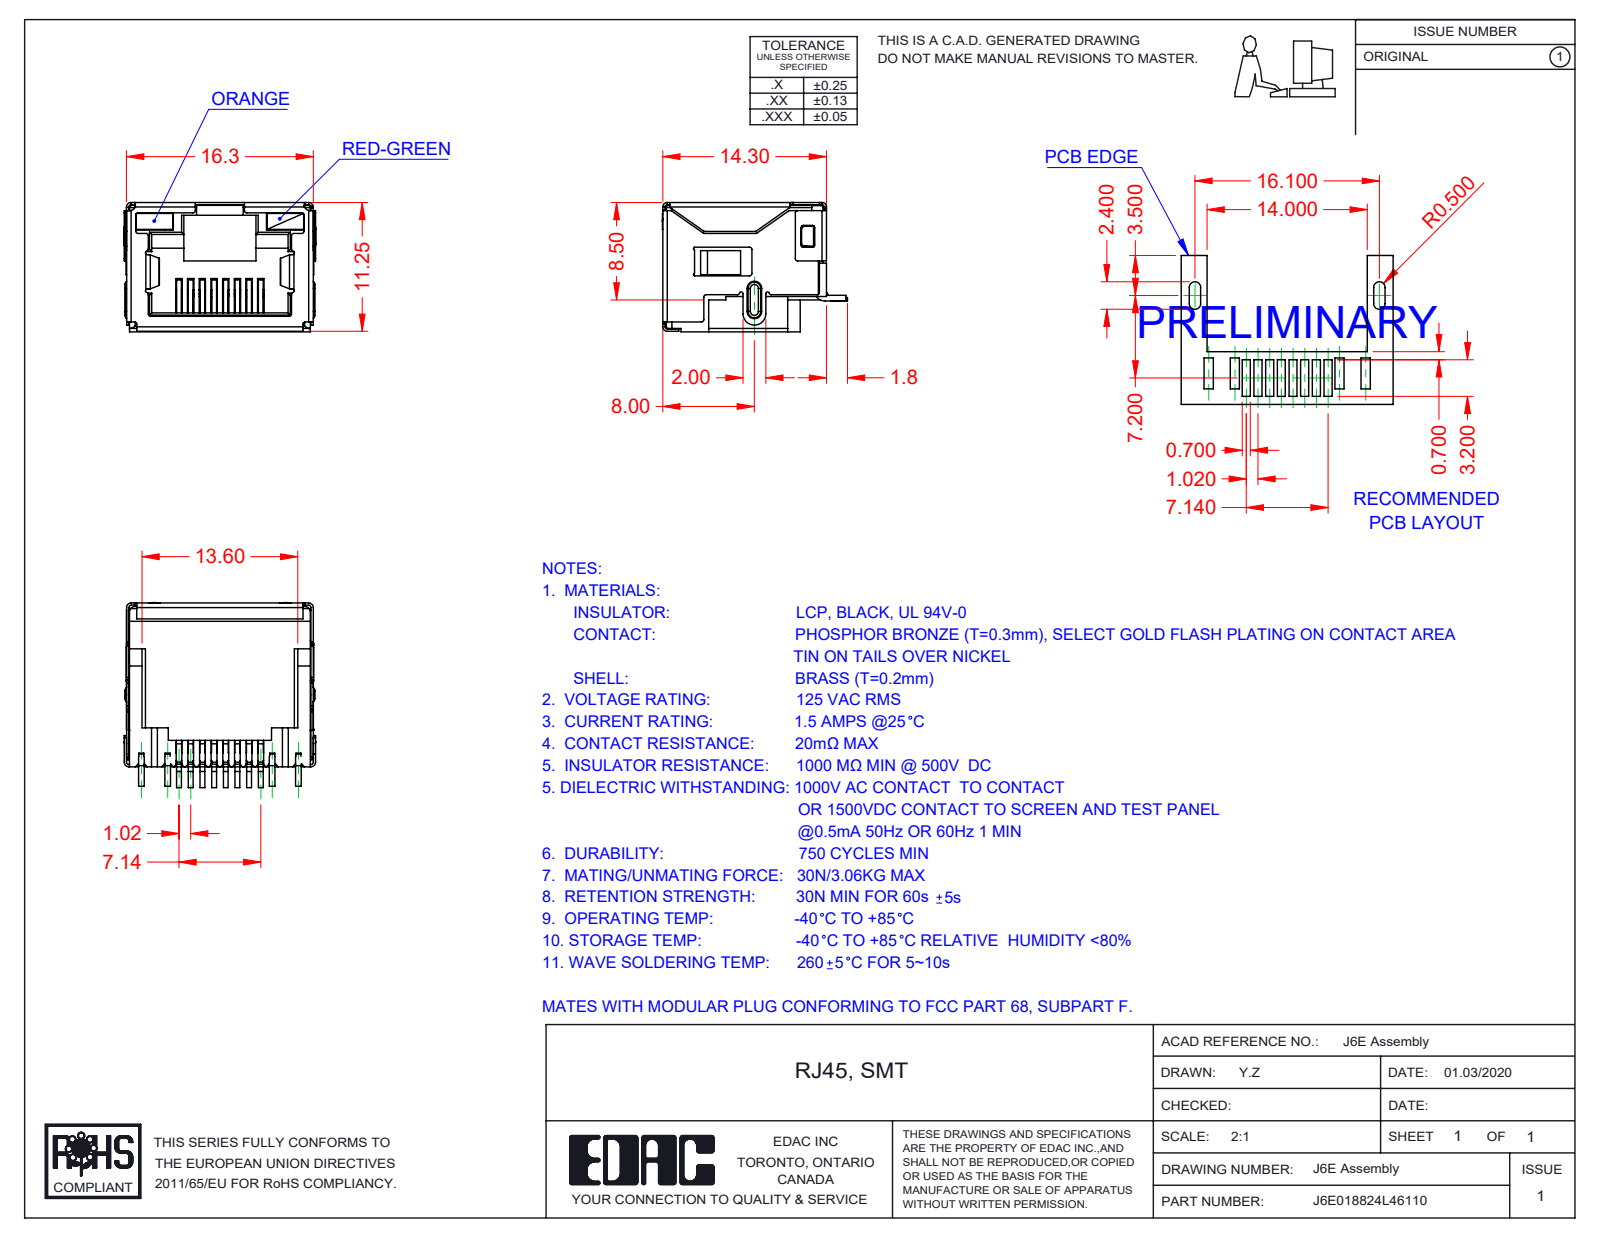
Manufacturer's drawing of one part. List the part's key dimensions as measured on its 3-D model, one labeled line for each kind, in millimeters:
Part name (STEP PRODUCT): 6E LED LH_4-Orange; J6E018824L46110; 6E Contacts; 6E LED RH_6-Red-Green (+2 more)
STEP written by: SolidWorks 2016 (CONFIG_CONTROL_DESIGN)
Units: millimetres
Bodies: 12 solids, 1498 faces (1099 planar, 349 cylindrical, 50 other)
Overall size (bounding box): 16.75 × 16.15 × 11.3
Volume: 1 109 mm³ · Surface area: 4 045 mm²
Partial cylindrical surfaces — rounded edges, fillets, slot ends (radius × count): R0.2 ×82, R0.25 ×17, R0.4 ×13, R0.5 ×13, R0.1 ×10, R0.15 ×7, R0.3 ×4, R1 ×3
Main face-to-face distances: 11.05, 16.05, 16.1, 15.85, 11.1, 11.3, 2.4, 0.7, 9.85, 0.49
